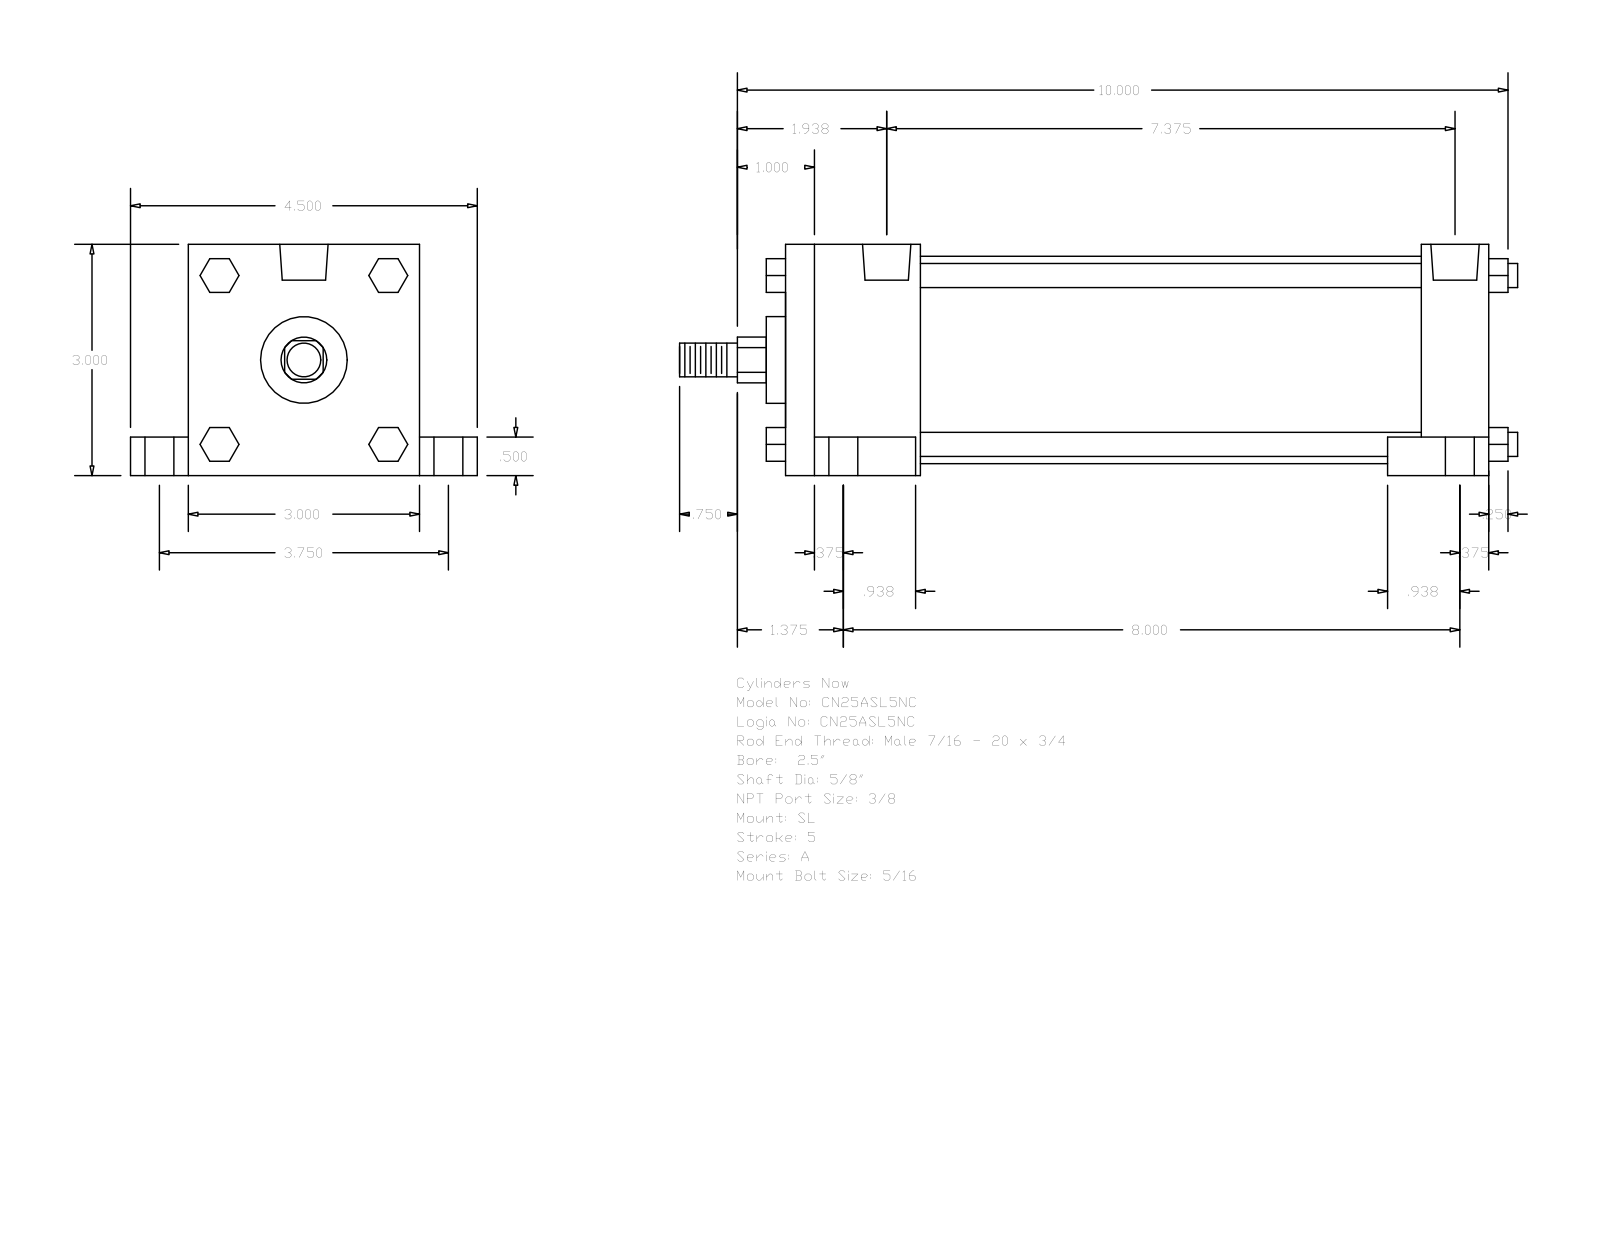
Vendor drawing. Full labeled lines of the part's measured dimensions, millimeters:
Part name (STEP PRODUCT): A_SL__0250_0.625
STEP written by: GSSL Pune (CONFIG_CONTROL_DESIGN)
Units: millimetres
Bodies: 0 solids, 148 faces (112 planar, 36 cylindrical, 0 other)
Overall size (bounding box): 276.23 × 114.3 × 76.2
Round holes (diameter × count): ⌀5.56 ×4, ⌀9.53 ×4, ⌀15.88 ×4, ⌀15.93 ×2
Round bosses / shafts (diameter × count): ⌀7.94 ×4, ⌀68.33 ×1, ⌀28.57 ×1, ⌀15.88 ×1, ⌀11.11 ×1
Partial cylindrical surfaces — rounded edges, fillets, slot ends (radius × count): R7.54 ×1
Main face-to-face distances: 76.2, 231.77, 44.45, 22.22, 187.32, 209.55, 165.1, 63.5, 12.7, 19.05
Hole centre spacings: 2.38, 47.63, 47.65, 49.09, 49.72, 95.24, 189.71, 192.09
